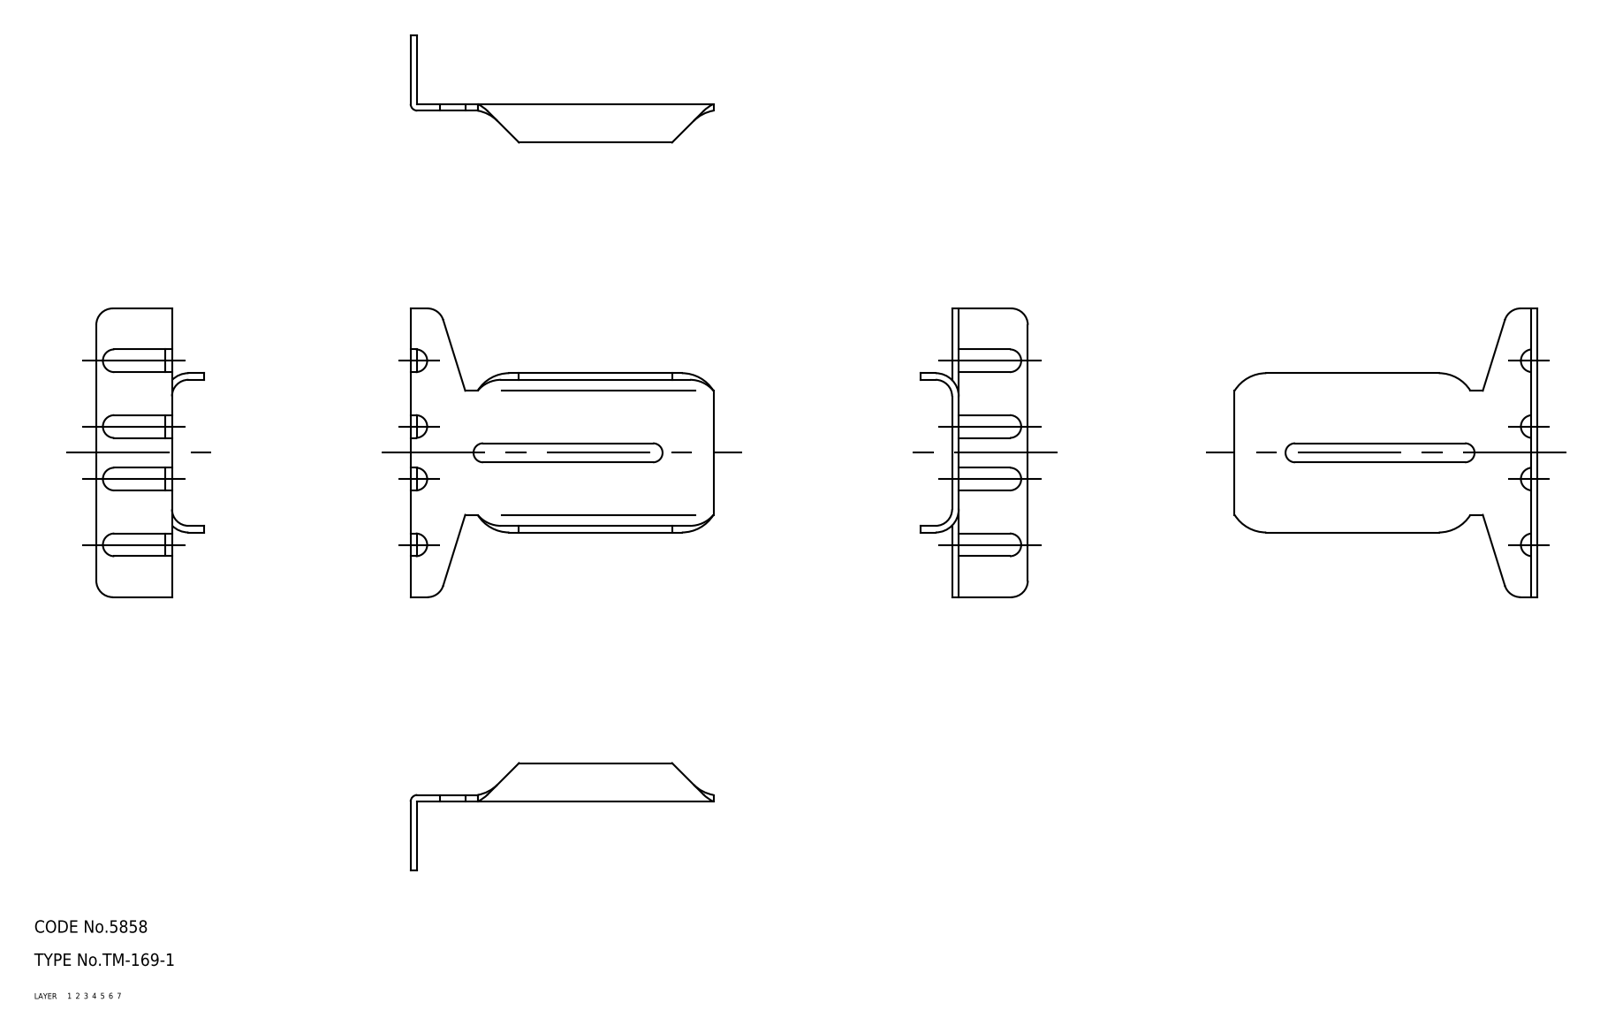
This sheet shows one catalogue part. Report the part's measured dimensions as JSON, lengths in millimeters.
{"part_name": "bracket", "step_written_by": "CADfix (AUTOMOTIVE_DESIGN)", "units": "millimeters", "bodies": {"solids": 1, "faces": 71, "planar": 0, "cylindrical": 0, "other": 71}, "overall_size": [73.2, 69.8, 26], "volume_mm3": 6600, "surface_area_mm2": 9197}
